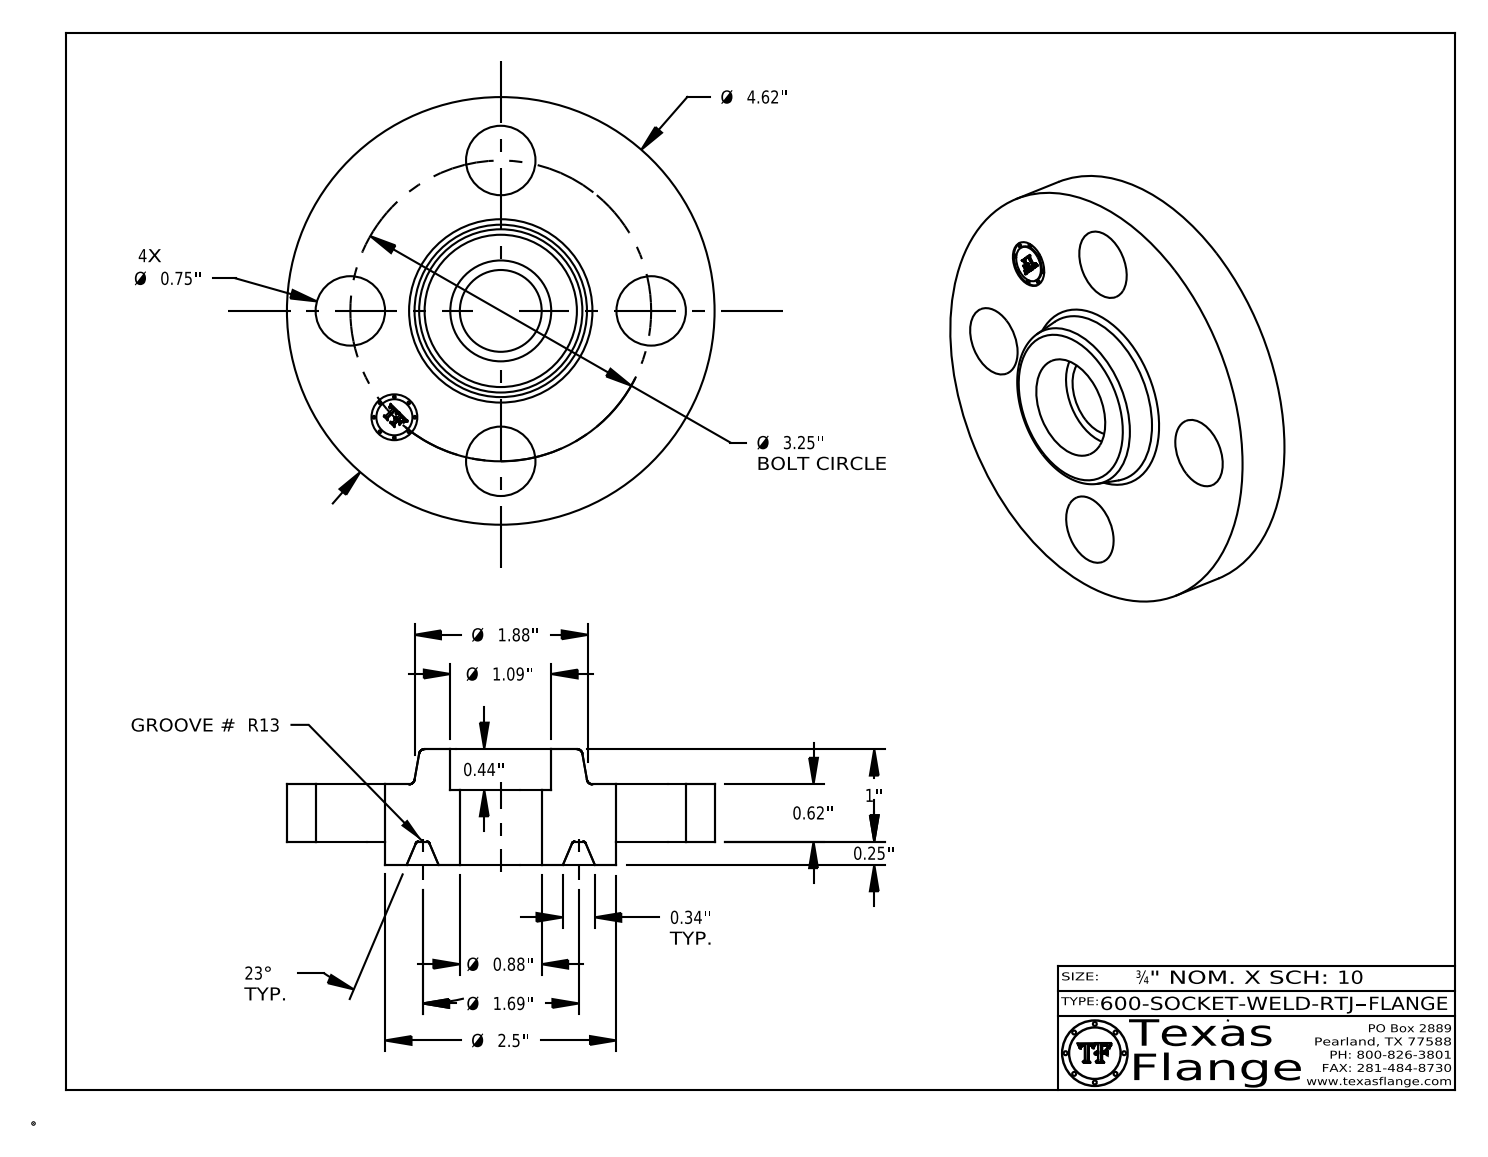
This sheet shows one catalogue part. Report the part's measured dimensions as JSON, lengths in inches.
{"part_name": "600-SOCKET-WELD-RTJ", "step_written_by": "CATIA V5 STEP AP214 (AUTOMOTIVE_DESIGN)", "units": "inches", "bodies": {"solids": 1, "faces": 422, "planar": 372, "cylindrical": 36, "other": 14}, "overall_size": [4.62, 4.62, 1.25], "volume_in3": 10.28, "surface_area_in2": 52.75, "round_holes": [[0.75, 4], [0.495, 1], [0.884, 1], [1.09, 1]], "round_bosses_or_shafts": [[0.03, 8], [4.62, 1], [2.5, 1], [0.39, 1]], "face_to_face_distances": [0.62, 0.25, 0.87, 1.25, 1, 0.38, 0.81, 0.56, 0.06, 0.44], "hole_center_spacings": [1.625, 2.298, 1.244, 3.003, 3.25]}
